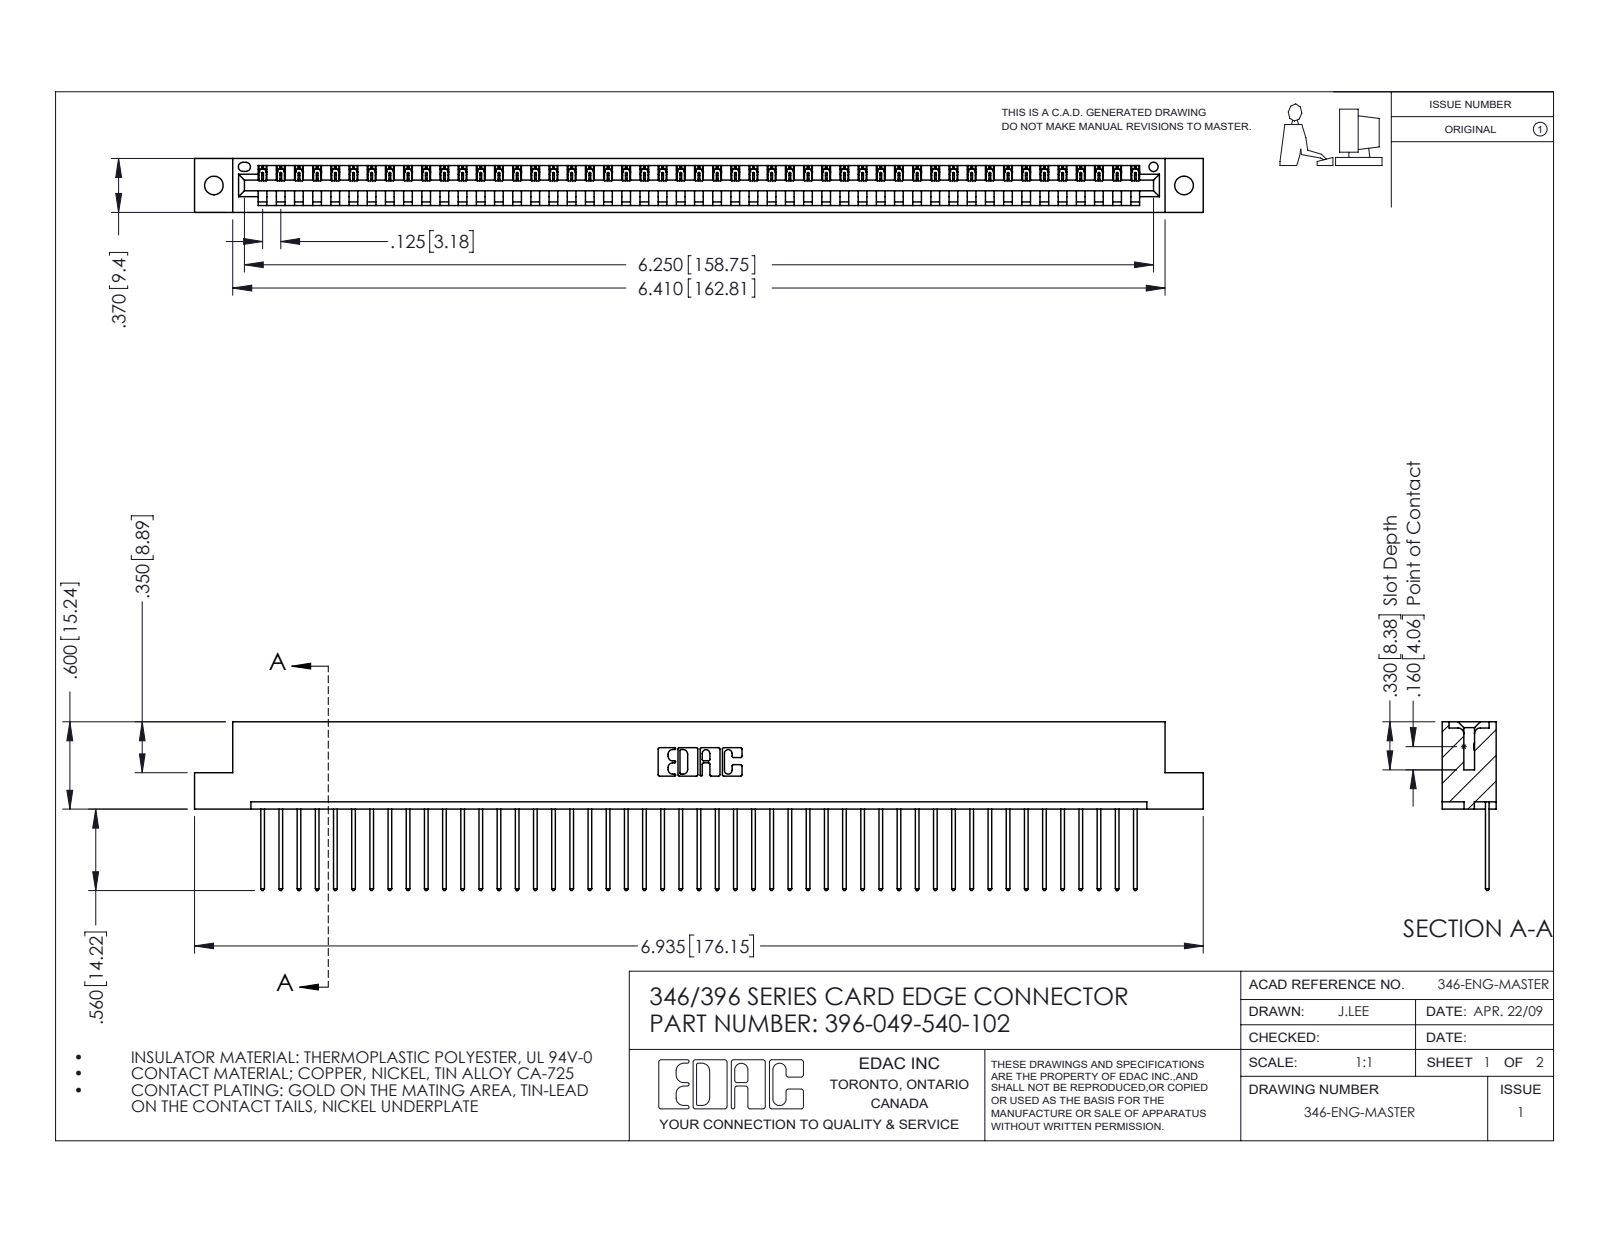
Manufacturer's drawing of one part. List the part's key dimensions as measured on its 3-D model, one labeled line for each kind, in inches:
Part name (STEP PRODUCT): 345-292-001_345-293-140; 346 Part_Flush Mounting Lugs - 0.128 Dia; 396-049-540-102
STEP written by: SolidWorks 2016 (CONFIG_CONTROL_DESIGN)
Units: inches
Bodies: 50 solids, 2964 faces (2036 planar, 928 cylindrical, 0 other)
Overall size (bounding box): 6.935 × 1.16 × 0.37
Volume: 1.034 in³ · Surface area: 33.26 in²
Round holes (diameter × count): ⌀0.128 ×2, ⌀0.064 ×1
Partial cylindrical surfaces — rounded edges, fillets, slot ends (radius × count): R0.006 ×98, R0.01 ×98, R0.01 ×22, R0.007 ×6, R0.031 ×6, R0.026 ×3, R0.031 ×2, R0.04 ×2
Main face-to-face distances: 0.048, 0.322, 0.37, 0.25, 0.072, 0.298, 0.025, 0.148, 0.222, 0.1
Hole centre spacings: 0.246, 6.461, 6.67
